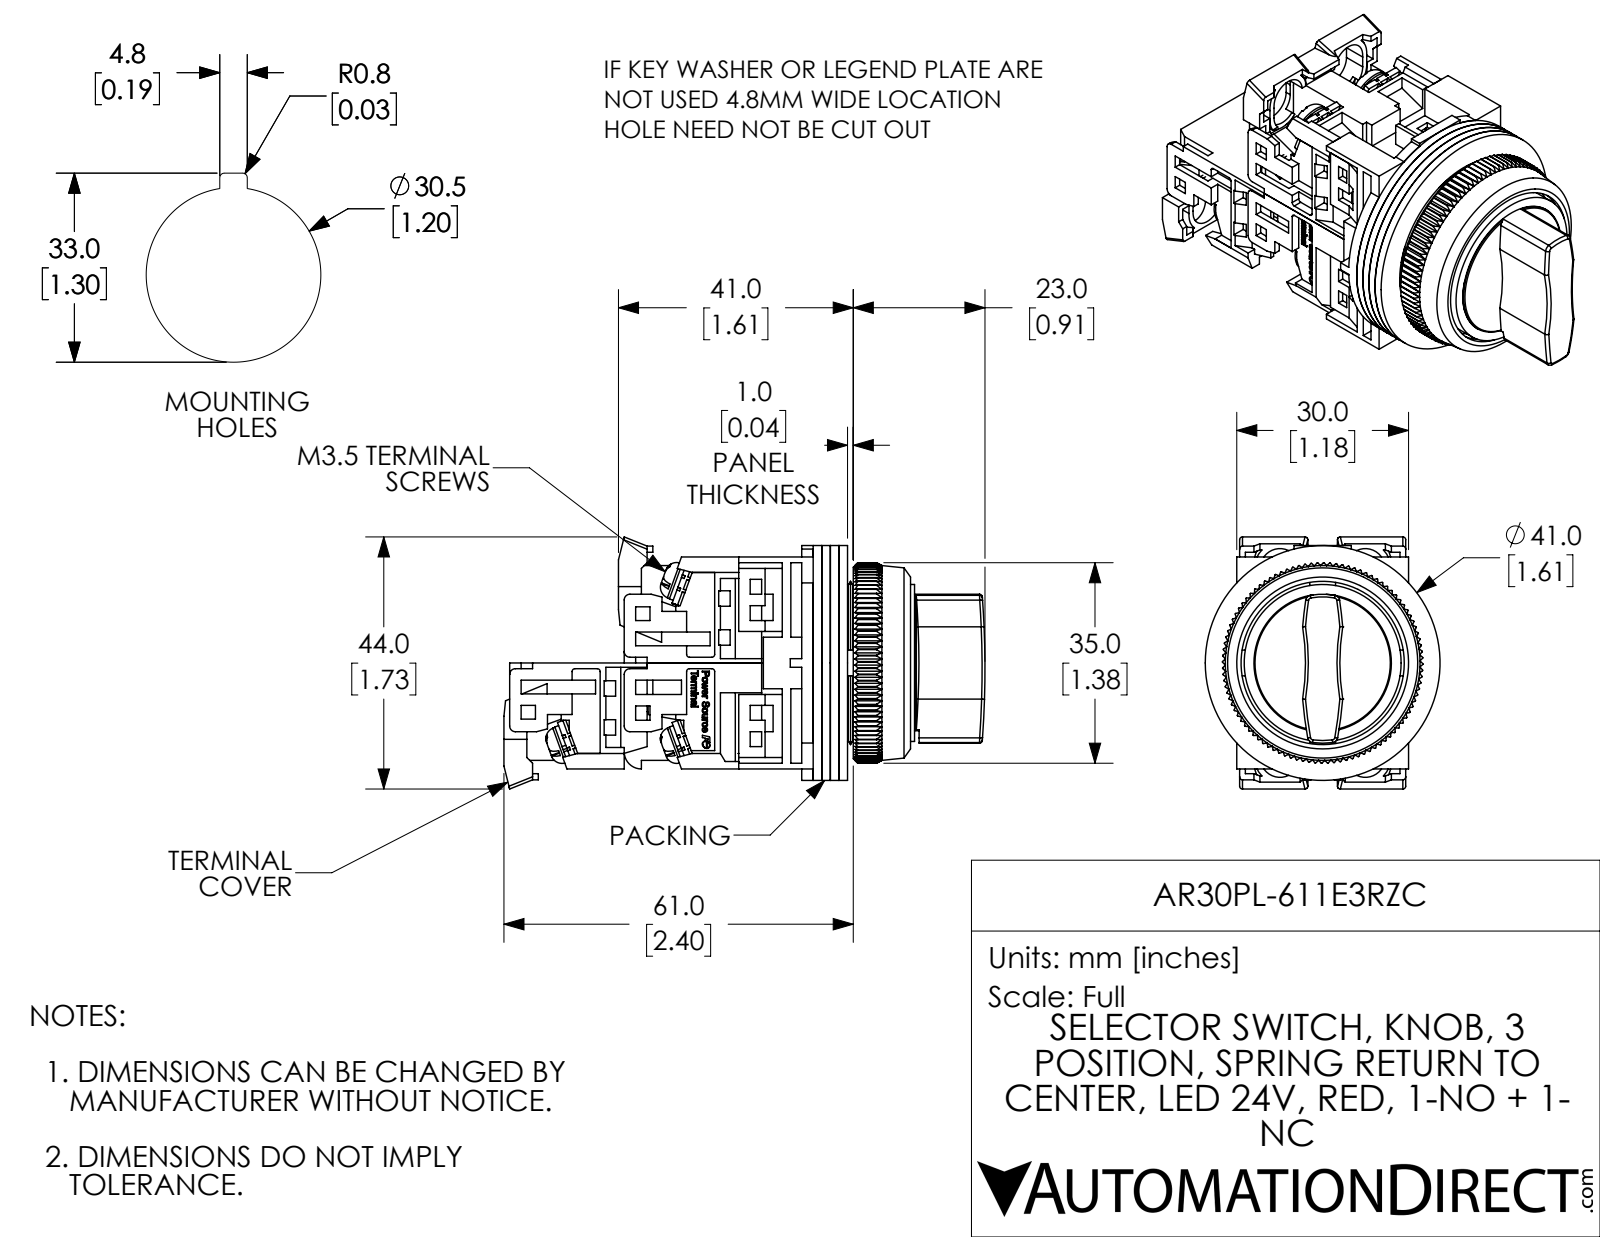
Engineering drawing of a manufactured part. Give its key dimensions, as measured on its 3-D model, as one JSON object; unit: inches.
{"part_name": "AR30PL-611E3RZC", "step_written_by": "SolidWorks 2017 (AUTOMOTIVE_DESIGN)", "units": "inches", "bodies": {"solids": 32, "faces": 2783, "planar": 2039, "cylindrical": 338, "other": 406}, "overall_size": [3.307, 1.732, 1.614], "volume_in3": 2.677, "surface_area_in2": 66.54, "round_holes": [[0.138, 10], [0.142, 6], [0.118, 1], [0.472, 1], [0.709, 1], [0.768, 1], [0.827, 1], [1.122, 1], [1.181, 1], [1.252, 1]], "round_bosses_or_shafts": [[0.26, 6], [0.138, 6], [0.063, 2], [1.614, 1], [1.15, 1], [1.079, 1], [0.945, 1], [0.886, 1]], "partial_cylinders_radius": [[0.059, 24], [0.02, 14], [0.039, 10], [0.138, 4], [0.177, 4], [0.118, 3], [1.575, 2], [2.953, 2]], "face_to_face_distances": [0.059, 0.118, 0.177, 0.039, 0.787, 0.063, 0.079, 0.02, 0.811, 0.689], "hole_center_spacings": [0.579, 0.269, 0.638, 0.61]}
